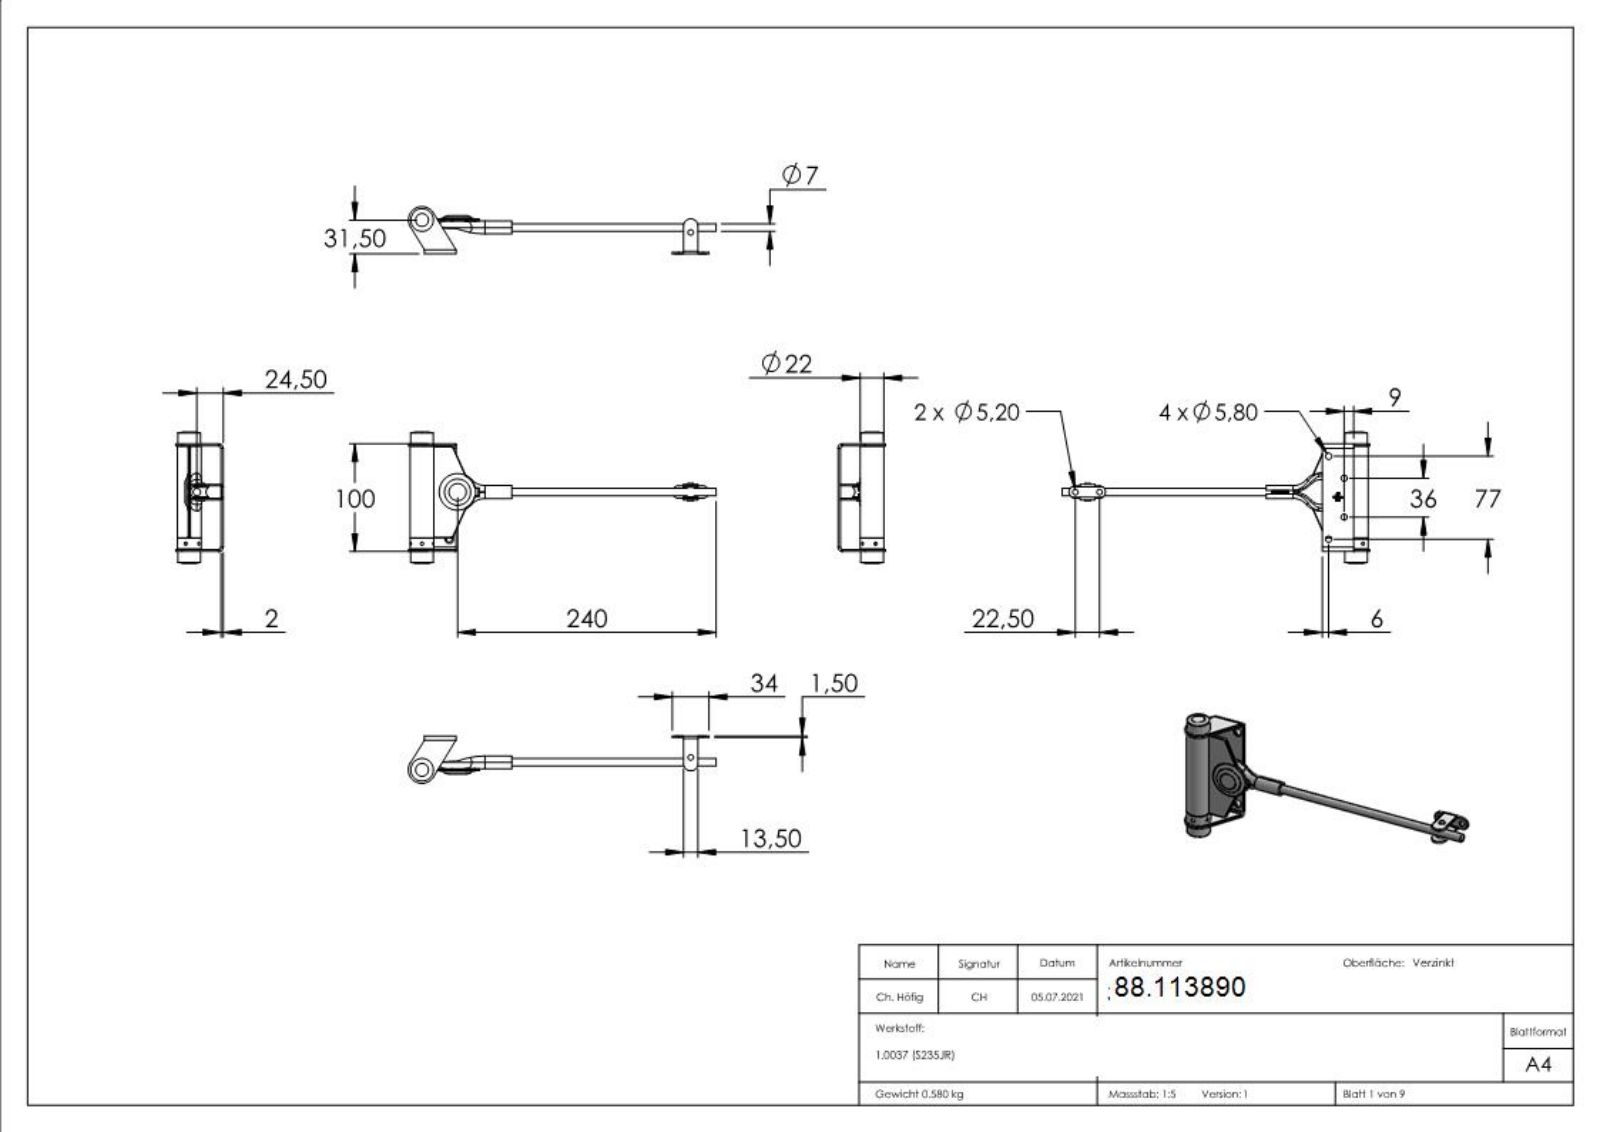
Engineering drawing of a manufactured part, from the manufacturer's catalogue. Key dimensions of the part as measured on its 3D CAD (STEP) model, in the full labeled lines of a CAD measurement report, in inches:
Part name (STEP PRODUCT): 389x Teil4; 389x Teil7_389x Teil7; 389x Teil6_389x Teil6; 389x Teil3 (+8 more)
STEP written by: SolidWorks 2018 (CONFIG_CONTROL_DESIGN)
Units: inches
Bodies: 9 solids, 596 faces (214 planar, 142 cylindrical, 240 other)
Overall size (bounding box): 11.24 × 4.803 × 1.732
Volume: 4.536 in³ · Surface area: 61.96 in²
Round holes (diameter × count): ⌀0.118 ×6, ⌀0.228 ×4, ⌀0.205 ×2, ⌀0.276 ×1, ⌀0.394 ×1
Round bosses / shafts (diameter × count): ⌀0.866 ×1, ⌀0.827 ×1, ⌀0.512 ×1, ⌀0.472 ×1, ⌀0.205 ×1, ⌀0.11 ×1
Partial cylindrical surfaces — rounded edges, fillets, slot ends (radius × count): R0.008 ×25, R0.02 ×17, R0.079 ×8, R0.039 ×2, R0.098 ×2, R0.157 ×2, R0.23 ×2, R0.828 ×2
Main face-to-face distances: 0.079, 1.201, 3.858, 1.122, 1.28, 3.937, 0.059, 3.78, 1.443, 1.904
Hole centre spacings: 0.985, 2.295, 0.886, 1.017, 1.067, 1.417, 2.429, 3.031
